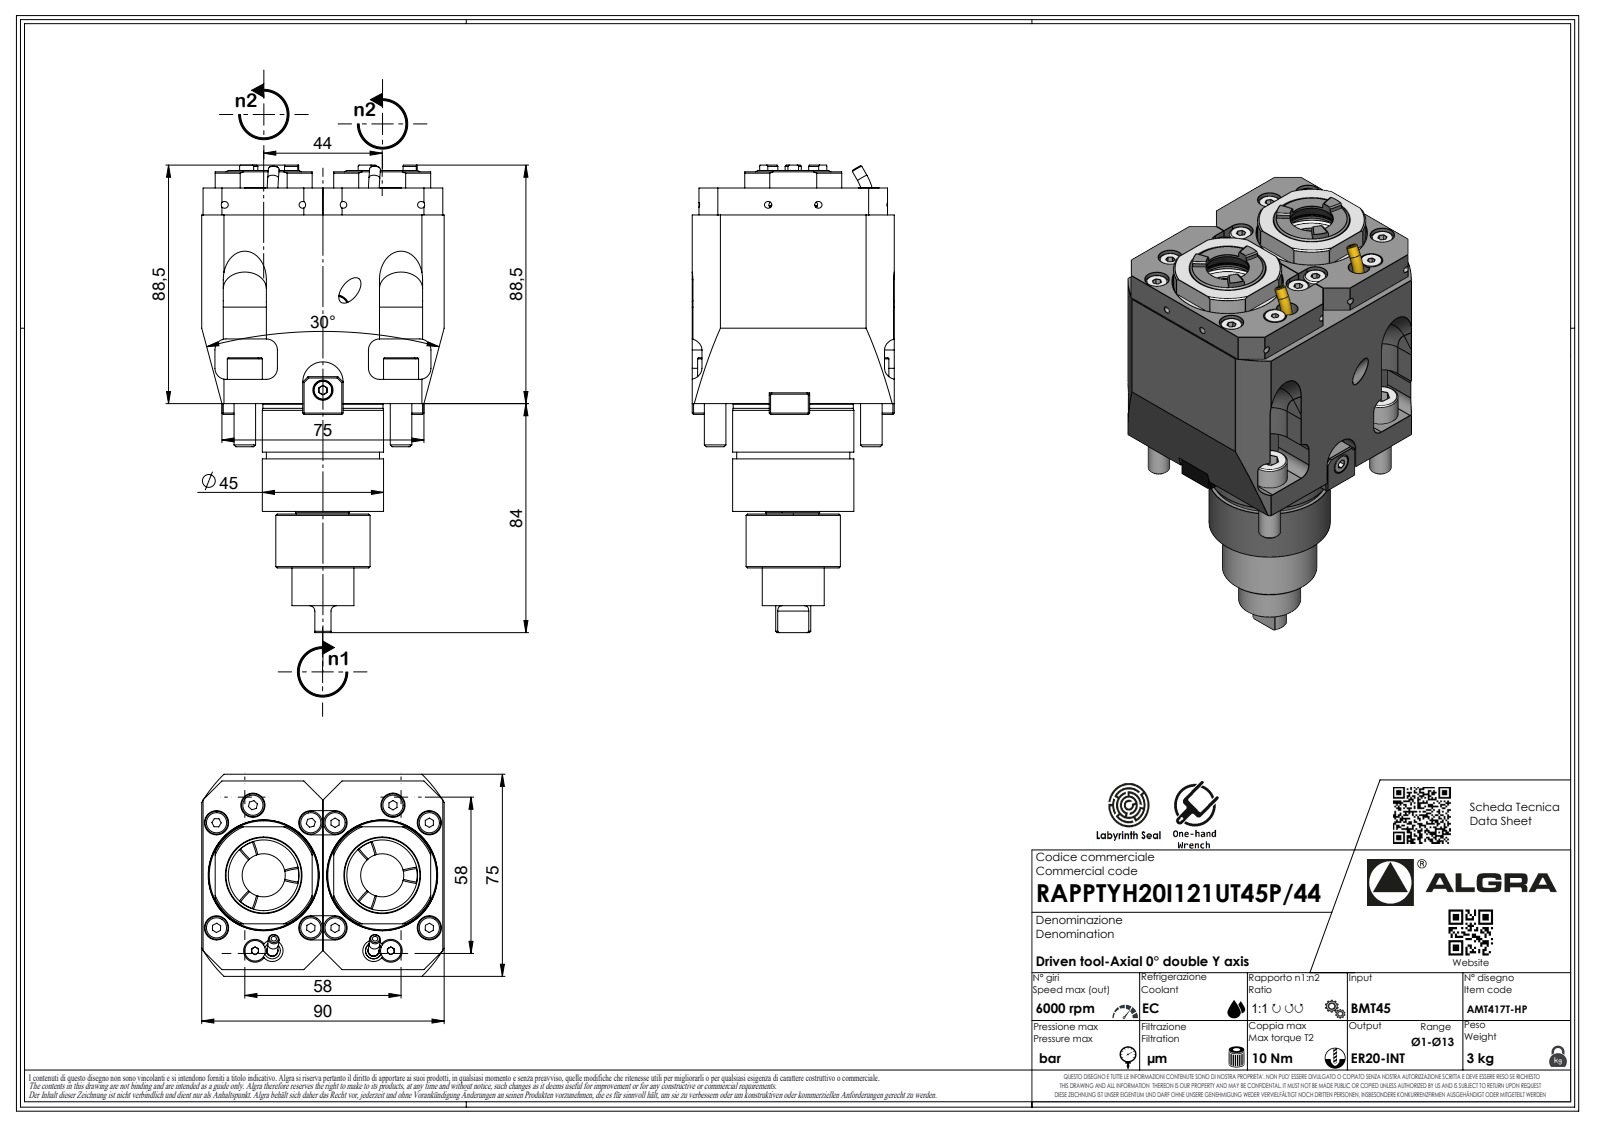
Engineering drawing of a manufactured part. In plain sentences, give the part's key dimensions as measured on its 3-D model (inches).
The part is named "RAPPTYH20I121UT45P44". Its 3-D file was written by "SolidWorks 2023 (AUTOMOTIVE_DESIGN)". It is 1 solid with 958 faces: 606 planar, 110 cylindrical and 242 other. Overall it measures 6.83 by 3.543 by 2.953 inches. Its volume is 35.21 cubic inches and its surface area 95.79 square inches. Round holes: 2 of diameter 0.63, 1 of diameter 0.062. Round bosses or shafts: 4 of diameter 0.512, 4 of diameter 0.315, 2 of diameter 0.157, 1 of diameter 1.772, 1 of diameter 1.654, 1 of diameter 1.378, 1 of diameter 0.906, 1 of diameter 0.654. Partial cylindrical surfaces (rounded edges, fillets, slot ends): 8 of radius 0.161, 8 of radius 0.315, 7 of radius 0.01, 7 of radius 0.015, 7 of radius 0.109, 6 of radius 1.281, 4 of radius 0.177, 2 of radius 0.079. The main face-to-face distances are 2.953, 3.15, 3.543, 0.63, 0.236, 1.575, 0.02, 0.098, 3.386, 0.531. The hole center spacings are 1.732.
